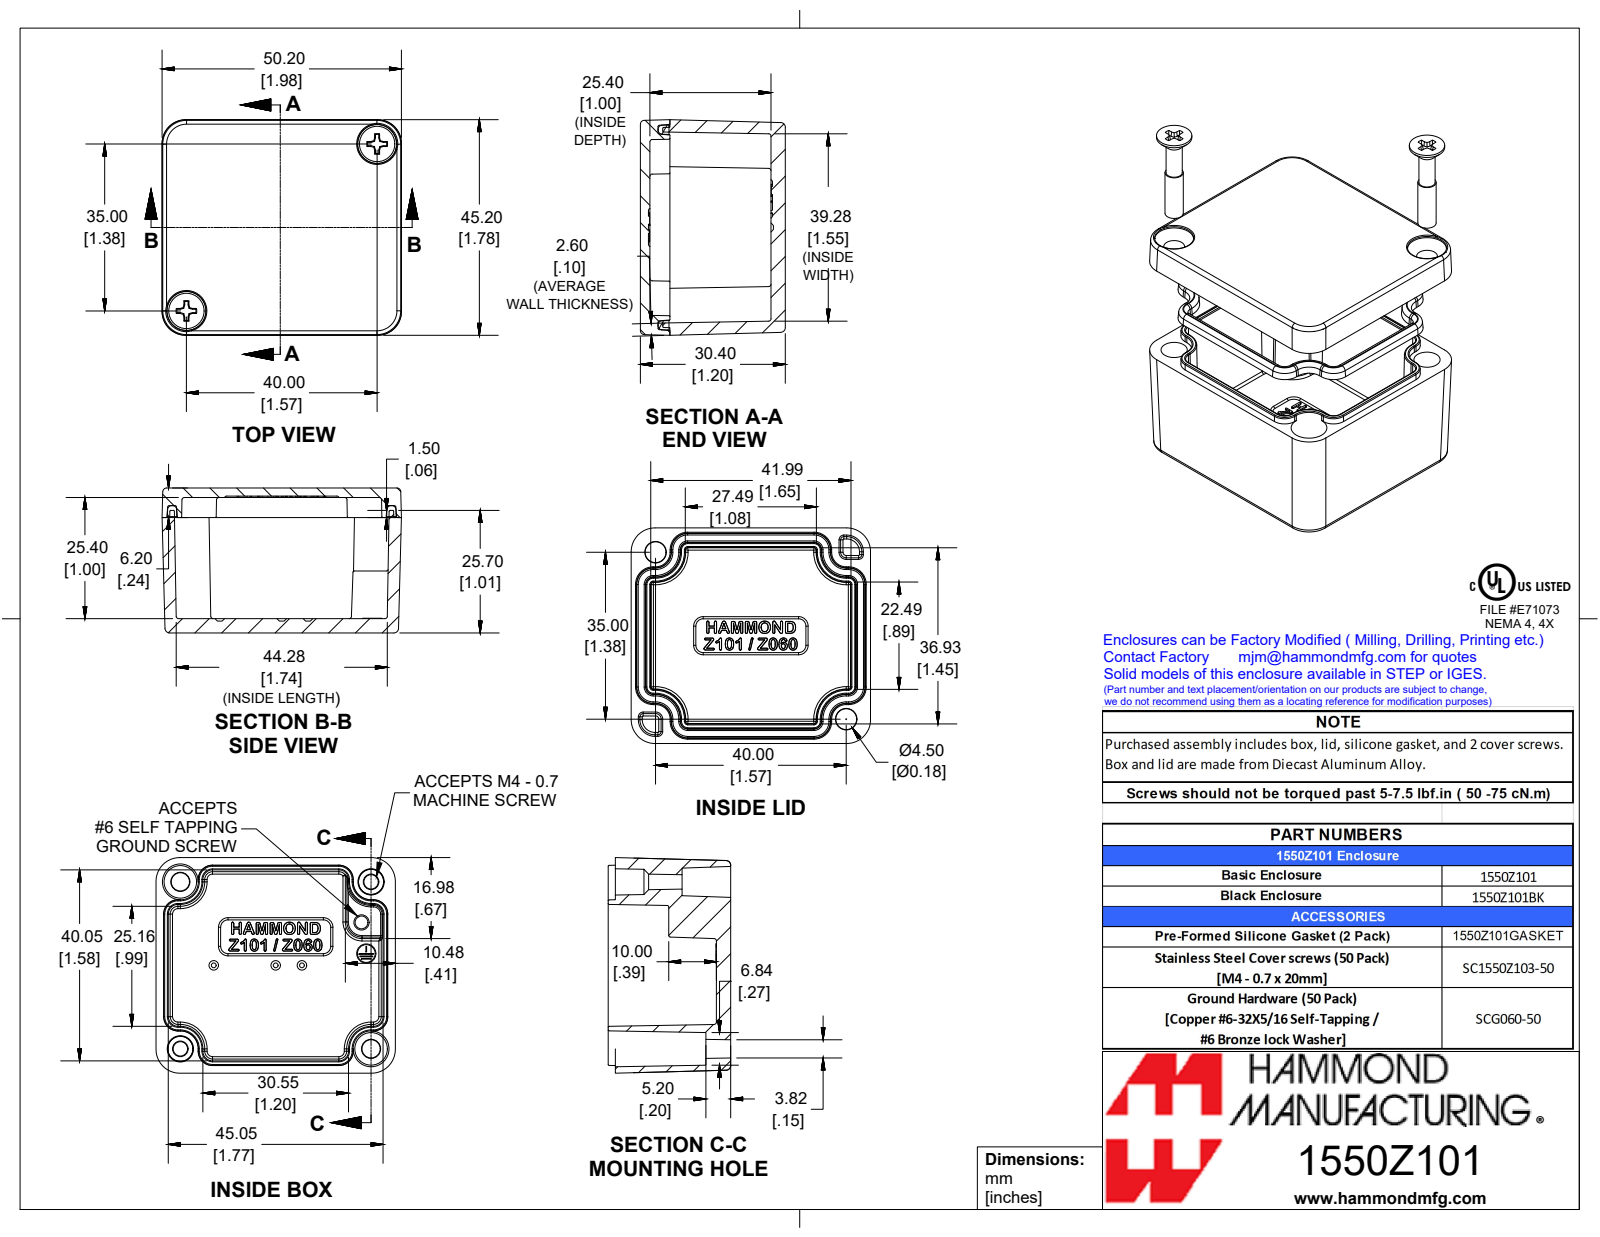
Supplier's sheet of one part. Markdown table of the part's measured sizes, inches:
| quantity | value |
| --- | --- |
| part name | 1550Z101 |
| STEP written by | SolidWorks 2019 (AUTOMOTIVE_DESIGN) |
| units | inches |
| bodies | 5 solids, 1237 faces (350 planar, 204 cylindrical, 683 other) |
| overall size | 1.976 × 1.78 × 1.197 |
| volume | 1.556 in³ |
| surface area | 35.87 in² |
| round bosses / shafts (diameter × count) | 0.295 × 2, 0.154 × 2, 0.13 × 2 |
| partial cylindrical surfaces (radius × count) | 0.008 × 40, 0.02 × 34, 0.012 × 22, 0.035 × 16, 0.197 × 8, 0.031 × 4, 0.039 × 4 |
| main face-to-face distances | 1.197, 0.118, 0.079, 1.079, 1.118, 1, 0.953, 0.835, 0.165, 0.244 |
